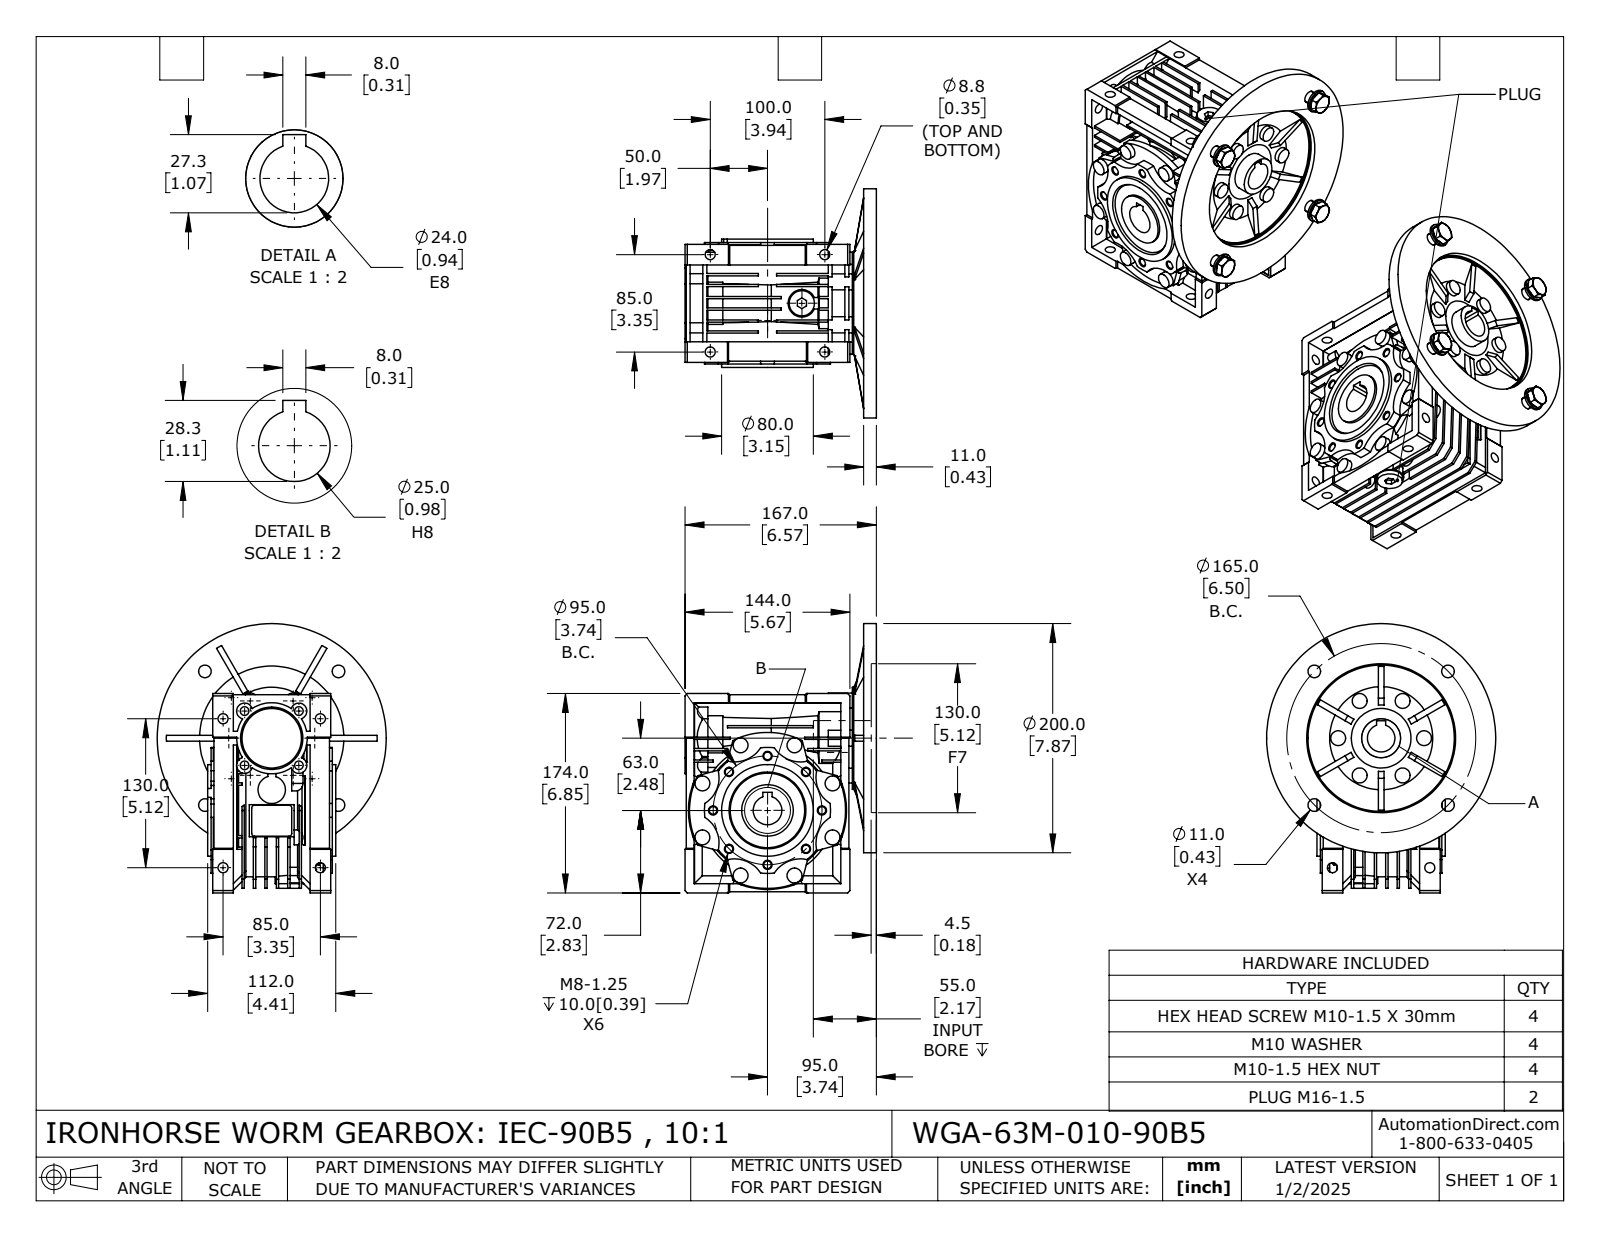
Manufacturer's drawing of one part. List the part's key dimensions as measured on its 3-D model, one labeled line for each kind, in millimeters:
Part name (STEP PRODUCT): WGA-63M-010-90B5
STEP written by: SolidWorks 2024 (CONFIG_CONTROL_DESIGN)
Units: millimetres
Bodies: 20 solids, 1529 faces (897 planar, 394 cylindrical, 238 other)
Overall size (bounding box): 235 × 200 × 183.43
Volume: 2 020 000 mm³ · Surface area: 402 901 mm²
Round holes (diameter × count): ⌀6.65 ×8, ⌀8.78 ×8, ⌀7.56 ×4, ⌀8.5 ×4, ⌀10 ×4, ⌀10.5 ×4, ⌀11 ×4, ⌀14.5 ×2, ⌀25 ×2, ⌀24 ×1, ⌀34 ×1, ⌀37 ×1
Round bosses / shafts (diameter × count): ⌀13 ×14, ⌀20 ×4, ⌀16 ×4, ⌀24 ×3, ⌀22 ×2, ⌀15.8 ×2, ⌀13.7 ×2, ⌀200 ×1
Partial cylindrical surfaces — rounded edges, fillets, slot ends (radius × count): R7 ×10, R27 ×8, R2.5 ×4, R8.35 ×1, R29.5 ×1, R30.5 ×1, R42 ×1, R46 ×1
Main face-to-face distances: 10, 8, 20, 2, 11, 30, 12, 7, 40, 18
Hole centre spacings: 36.36, 47.5, 67.18, 87.77, 89.05, 33.5, 47.38, 49
